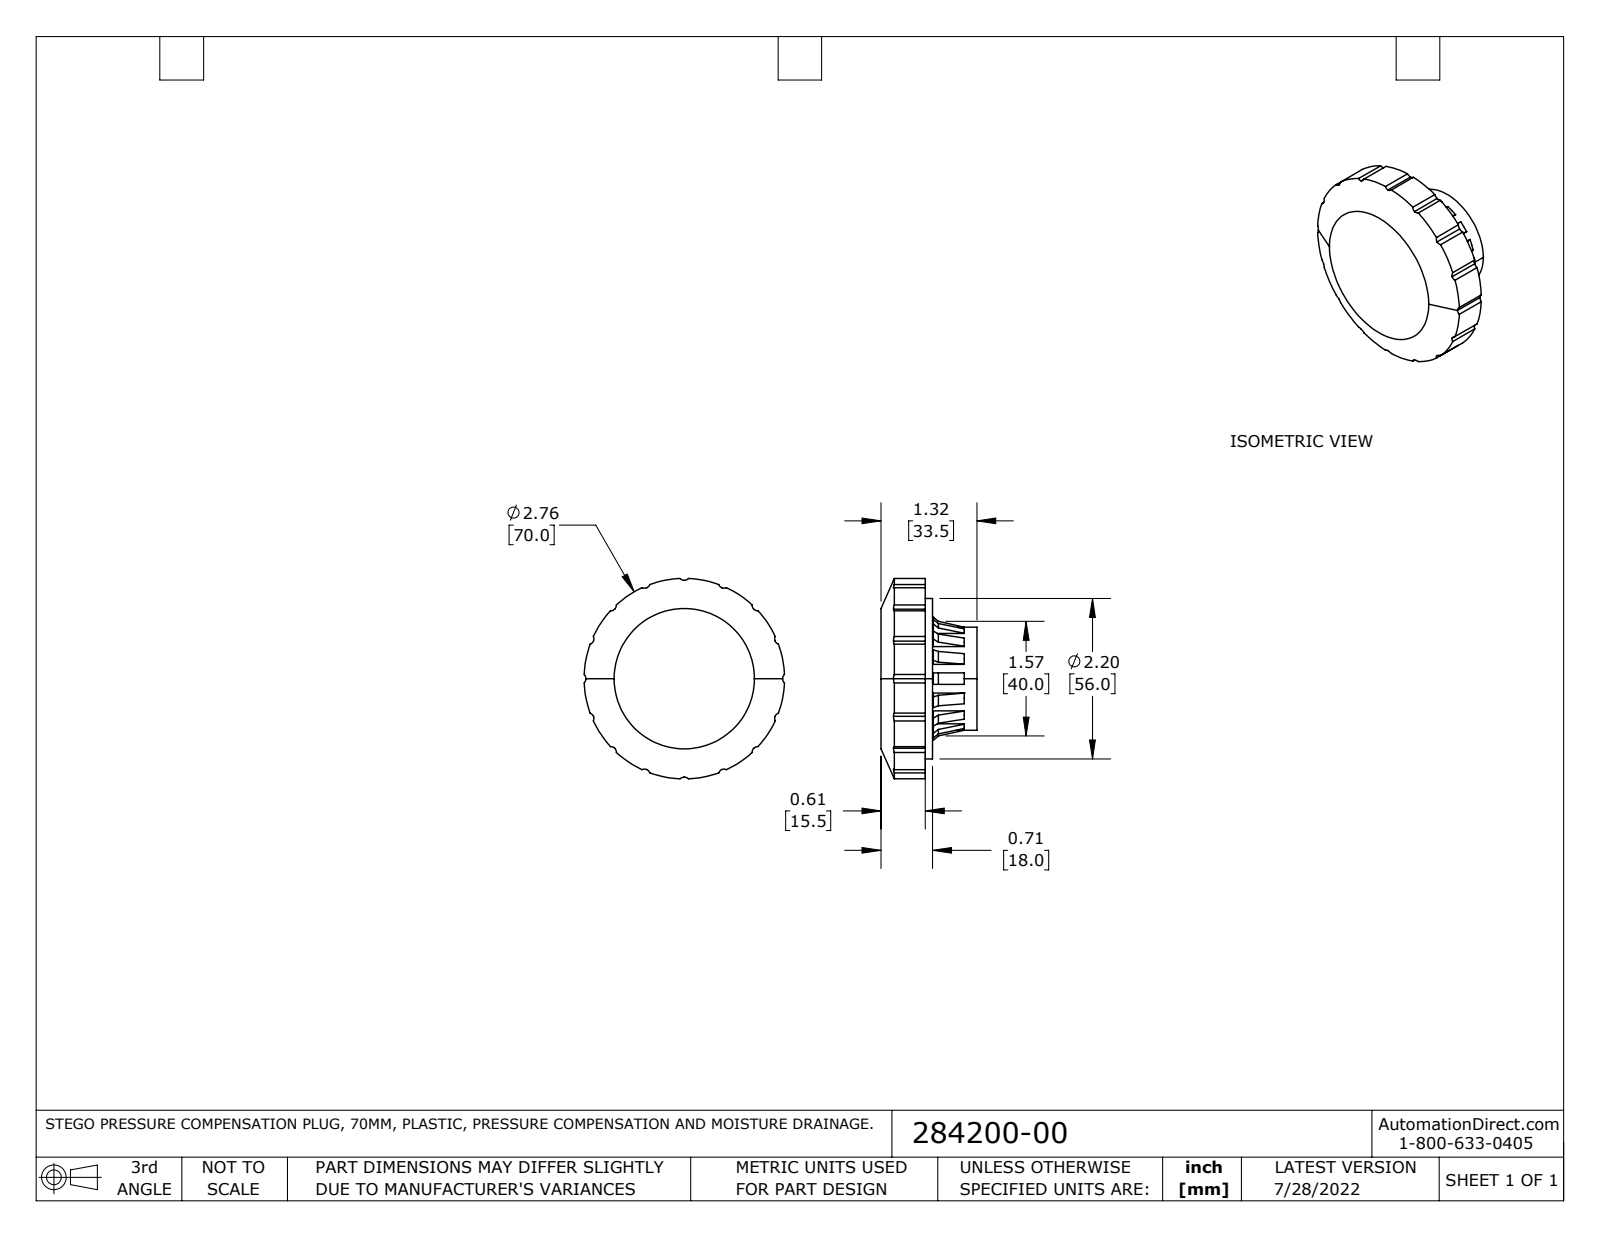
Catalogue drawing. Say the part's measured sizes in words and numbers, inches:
The part is named "284200-00_Default". Its 3-D file was written by "SolidWorks 2021 (CONFIG_CONTROL_DESIGN)". It is 1 solid with 224 faces: 134 planar, 88 cylindrical and 2 other. Overall it measures 2.754 by 2.754 by 1.319 inches. Its volume is 3.753 cubic inches and its surface area 26.77 square inches. Round holes: 16 of diameter 0.118, 1 of diameter 1.205, 1 of diameter 2.618. Round bosses or shafts: 1 of diameter 2.205, 1 of diameter 1.417. Partial cylindrical surfaces (rounded edges, fillets, slot ends): 16 of radius 0.079, 1 of radius 1.378. The main face-to-face distances are 0.709, 0.355, 0.354, 0.122, 0.477, 0.831, 0.61, 0.22, 0.098, 0.256. The hole center spacings are 0.47, 0.923, 1.206, 1.339, 1.34, 1.705, 2.005, 2.005.
